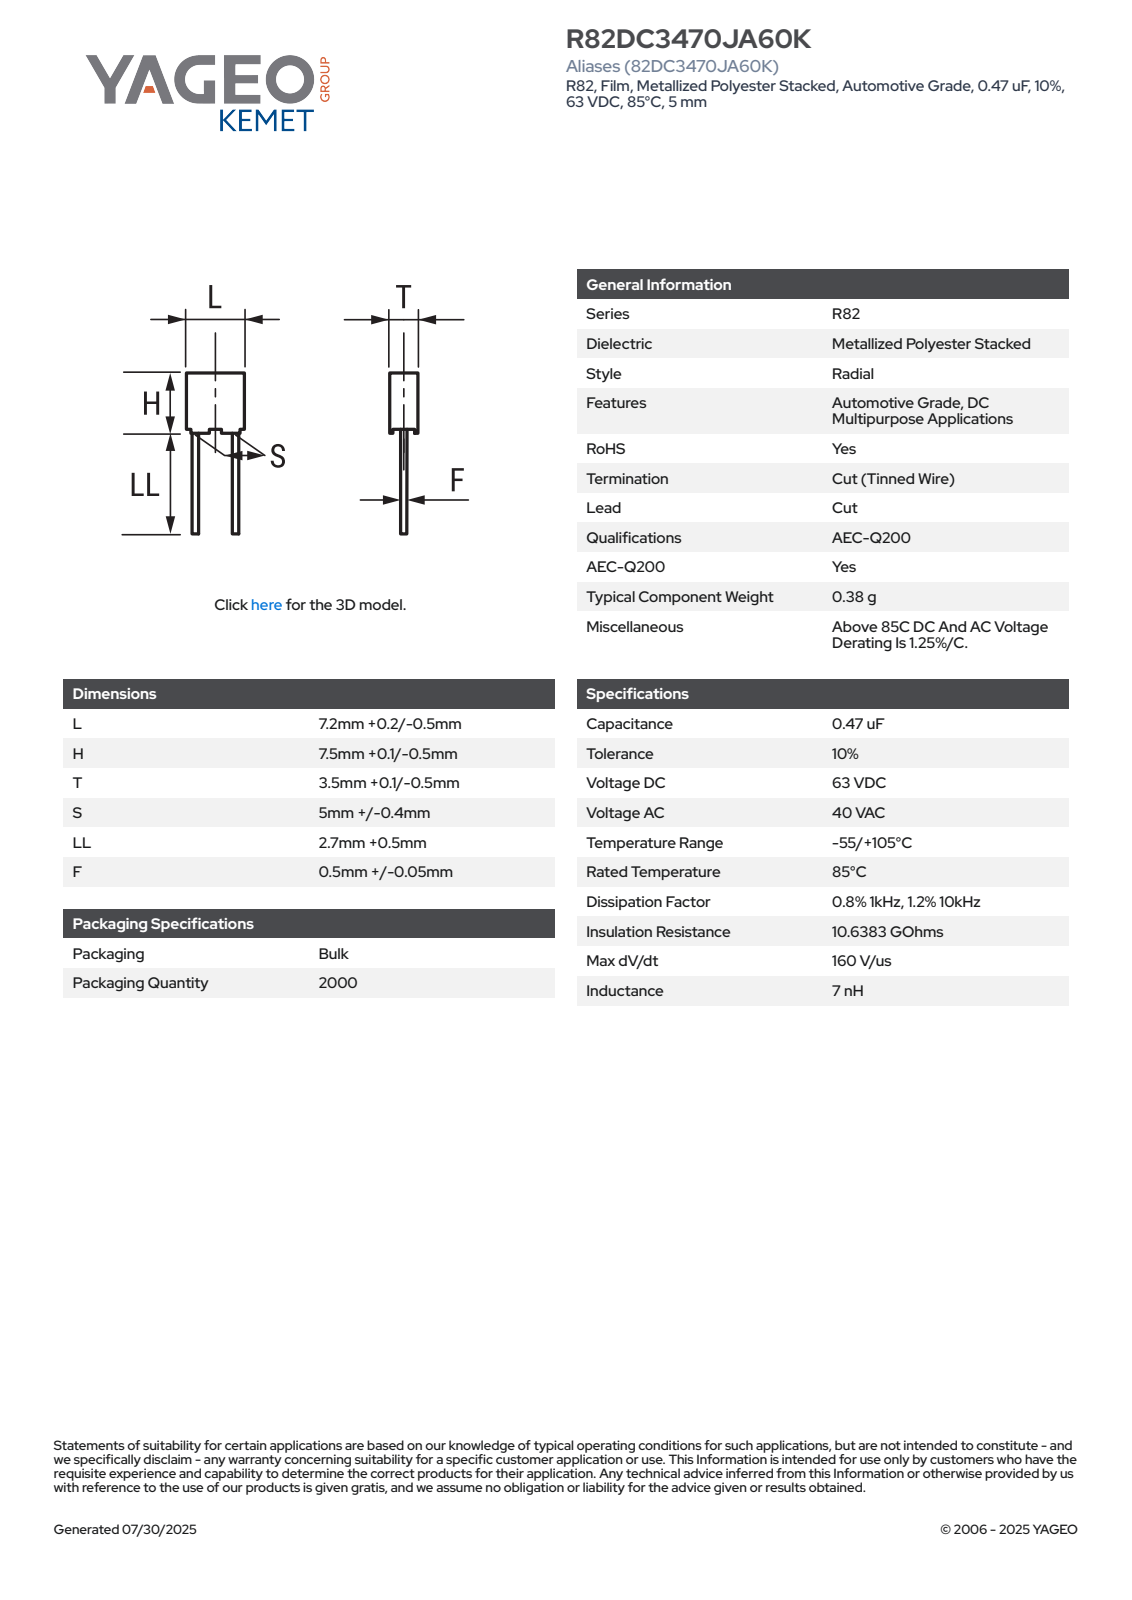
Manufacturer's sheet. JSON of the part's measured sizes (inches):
{"part_name": "CFR_RB3_7.2X7.5X3.5_L7.4H7.6T3.6S5LL3.2F0.55", "step_written_by": "SolidWorks 2014 (AUTOMOTIVE_DESIGN)", "units": "inches", "bodies": {"solids": 4, "faces": 85, "planar": 77, "cylindrical": 8, "other": 0}, "overall_size": [0.425, 0.291, 0.142], "volume_in3": 0.011, "surface_area_in2": 0.383, "round_bosses_or_shafts": [[0.022, 2]], "partial_cylinders_radius": [[0.02, 4]], "face_to_face_distances": [0.142, 0.291, 0.27, 0.132, 0.122, 0.281, 0.03, 0.299, 0.272, 0.019]}
